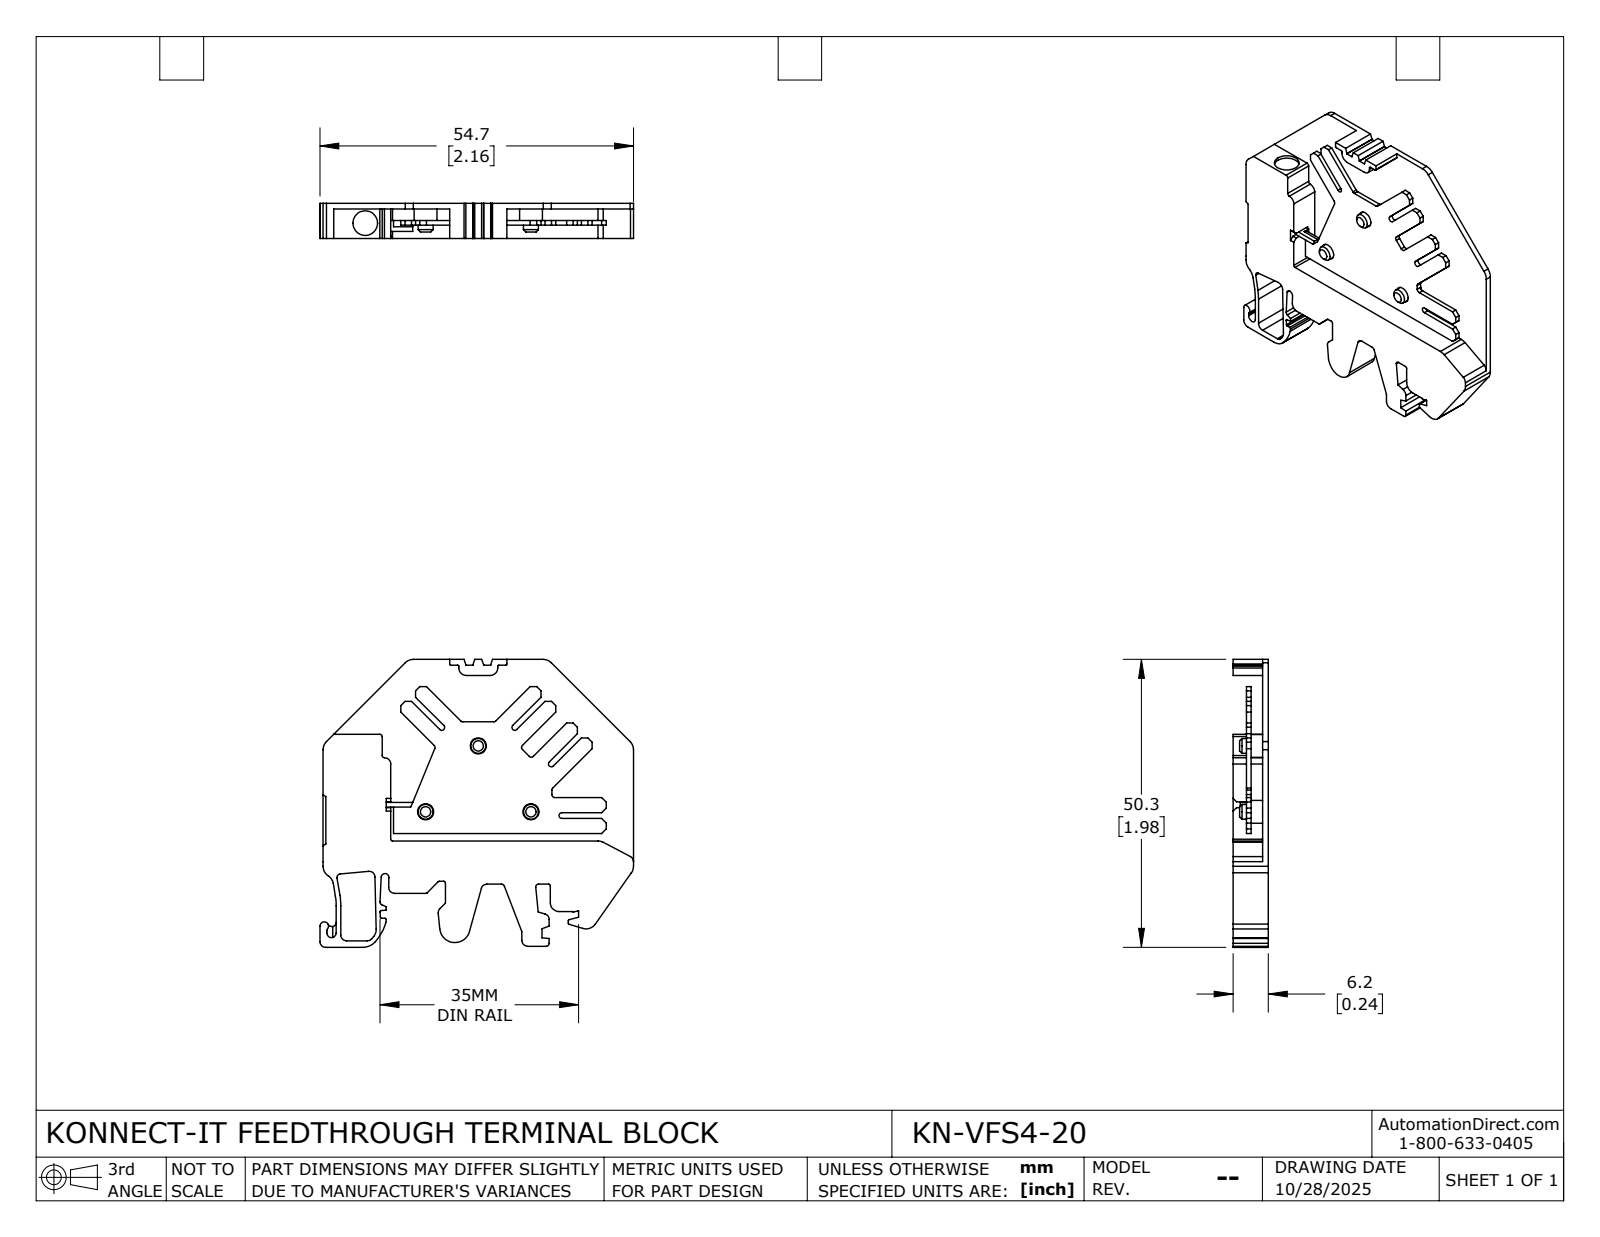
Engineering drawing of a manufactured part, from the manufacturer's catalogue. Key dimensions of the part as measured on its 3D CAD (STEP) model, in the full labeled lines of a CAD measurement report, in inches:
Part name (STEP PRODUCT): KN-VFS4-20
STEP written by: SolidWorks 2024 (CONFIG_CONTROL_DESIGN)
Units: inches
Bodies: 1 solid, 259 faces (153 planar, 100 cylindrical, 6 other)
Overall size (bounding box): 2.156 × 1.979 × 0.242
Volume: 0.421 in³ · Surface area: 11.69 in²
Round holes (diameter × count): ⌀0.11 ×3, ⌀0.169 ×1
Round bosses / shafts (diameter × count): ⌀0.157 ×3, ⌀0.102 ×3
Partial cylindrical surfaces — rounded edges, fillets, slot ends (radius × count): R0.02 ×15, R0.008 ×10, R0.079 ×10, R0.039 ×8, R0.012 ×5, R0.016 ×2, R0.03 ×2, R0.039 ×2
Main face-to-face distances: 0.039, 0.242, 0.203, 0.031, 0.11, 0.15, 0.093, 0.079, 0.118, 0.124
Hole centre spacings: 0.58, 0.724
